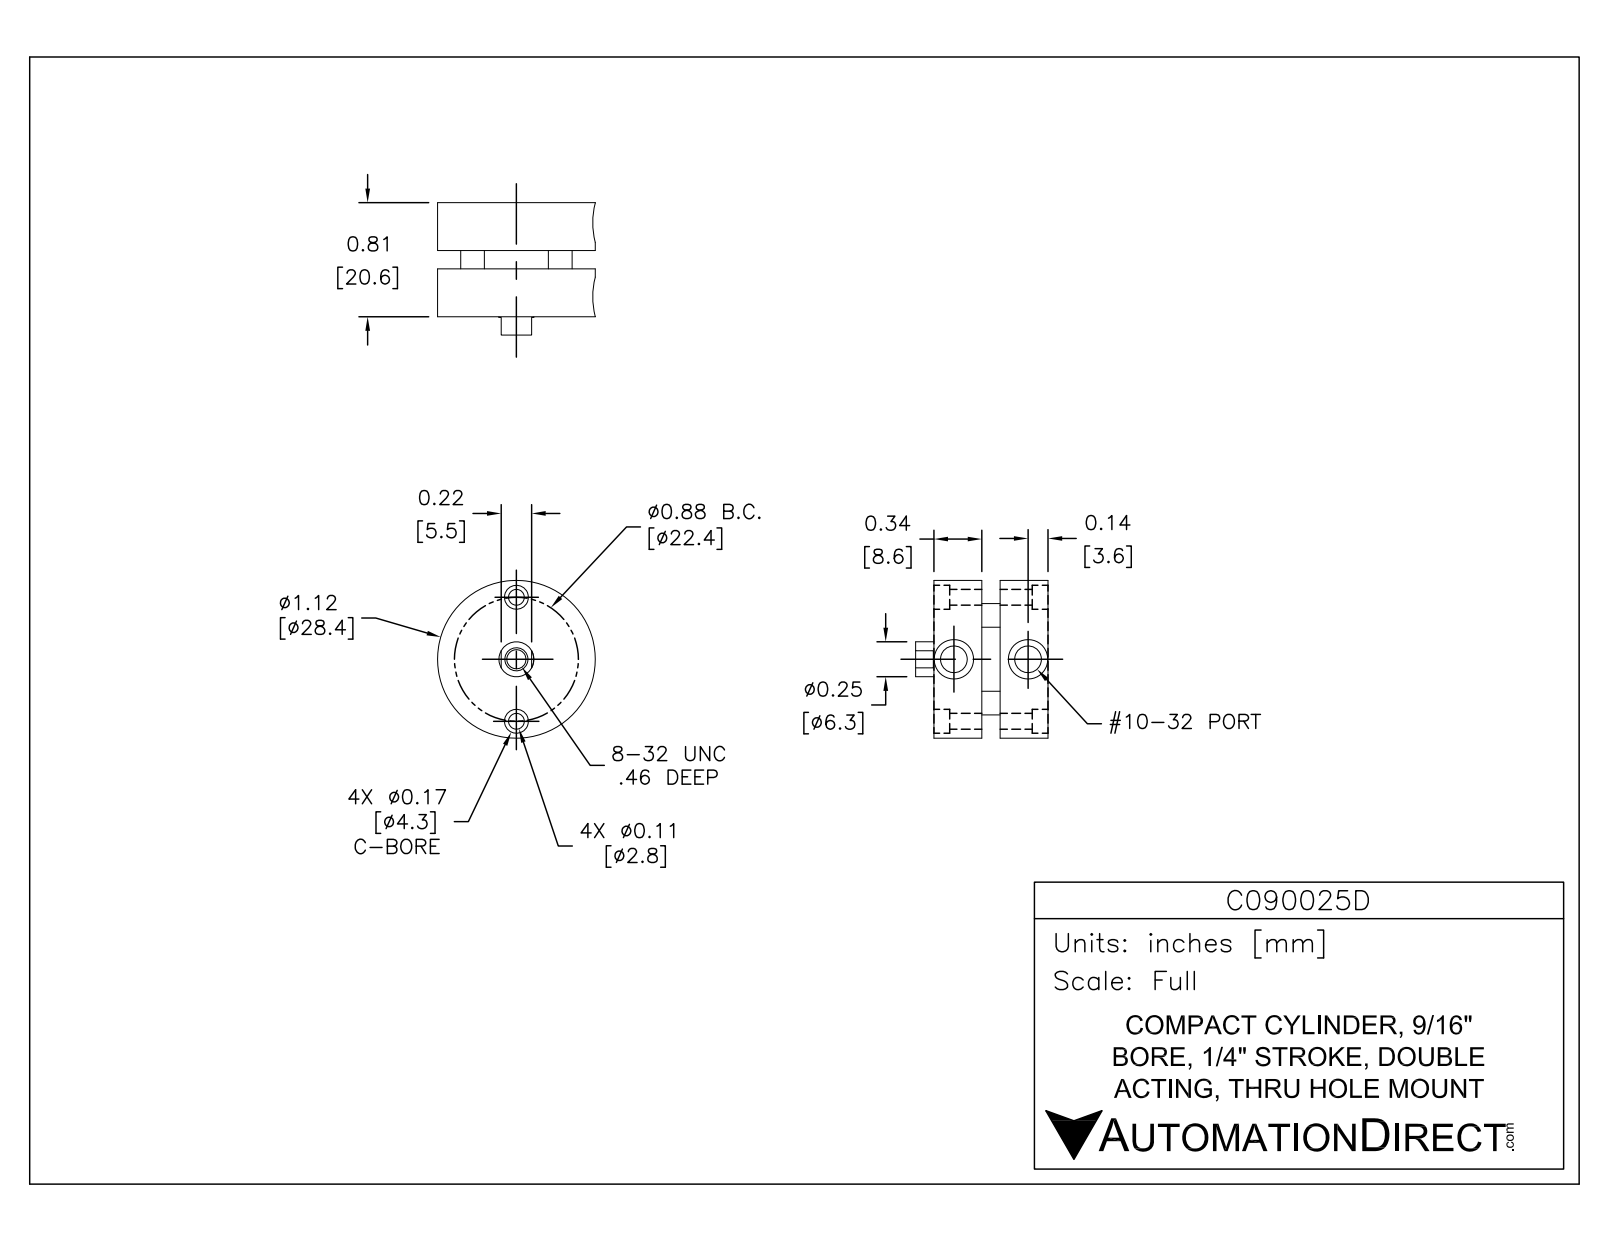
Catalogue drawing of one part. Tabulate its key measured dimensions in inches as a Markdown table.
| quantity | value |
| --- | --- |
| part name | C090025D-rod_part; C090025D-FO1_BM_r; C090025D; C090025D-FO1_BM_rod (+3 more) |
| STEP written by | SolidWorks 2014 (AUTOMOTIVE_DESIGN) |
| units | inches |
| bodies | 9 solids, 145 faces (47 planar, 88 cylindrical, 10 other) |
| overall size | 1.12 × 1.12 × 0.94 |
| volume | 0.645 in³ |
| surface area | 11.69 in² |
| round holes (diameter × count) | 0.12 × 6, 0.156 × 2, 0.188 × 2, 0.134 × 1, 0.25 × 1, 0.252 × 1, 0.562 × 1, 0.61 × 1 |
| round bosses / shafts (diameter × count) | 0.24 × 4, 1.12 × 1 |
| partial cylindrical surfaces (radius × count) | 0.156 × 2 |
| main face-to-face distances | 0.1, 0.23, 0.81, 0.47, 0.34, 0.34, 0.13, 0.47, 0.24, 0.57 |
| hole center spacings | 0.337, 0.44, 0.622, 0.813, 0.44, 0.88, 0.53, 0.88 |
